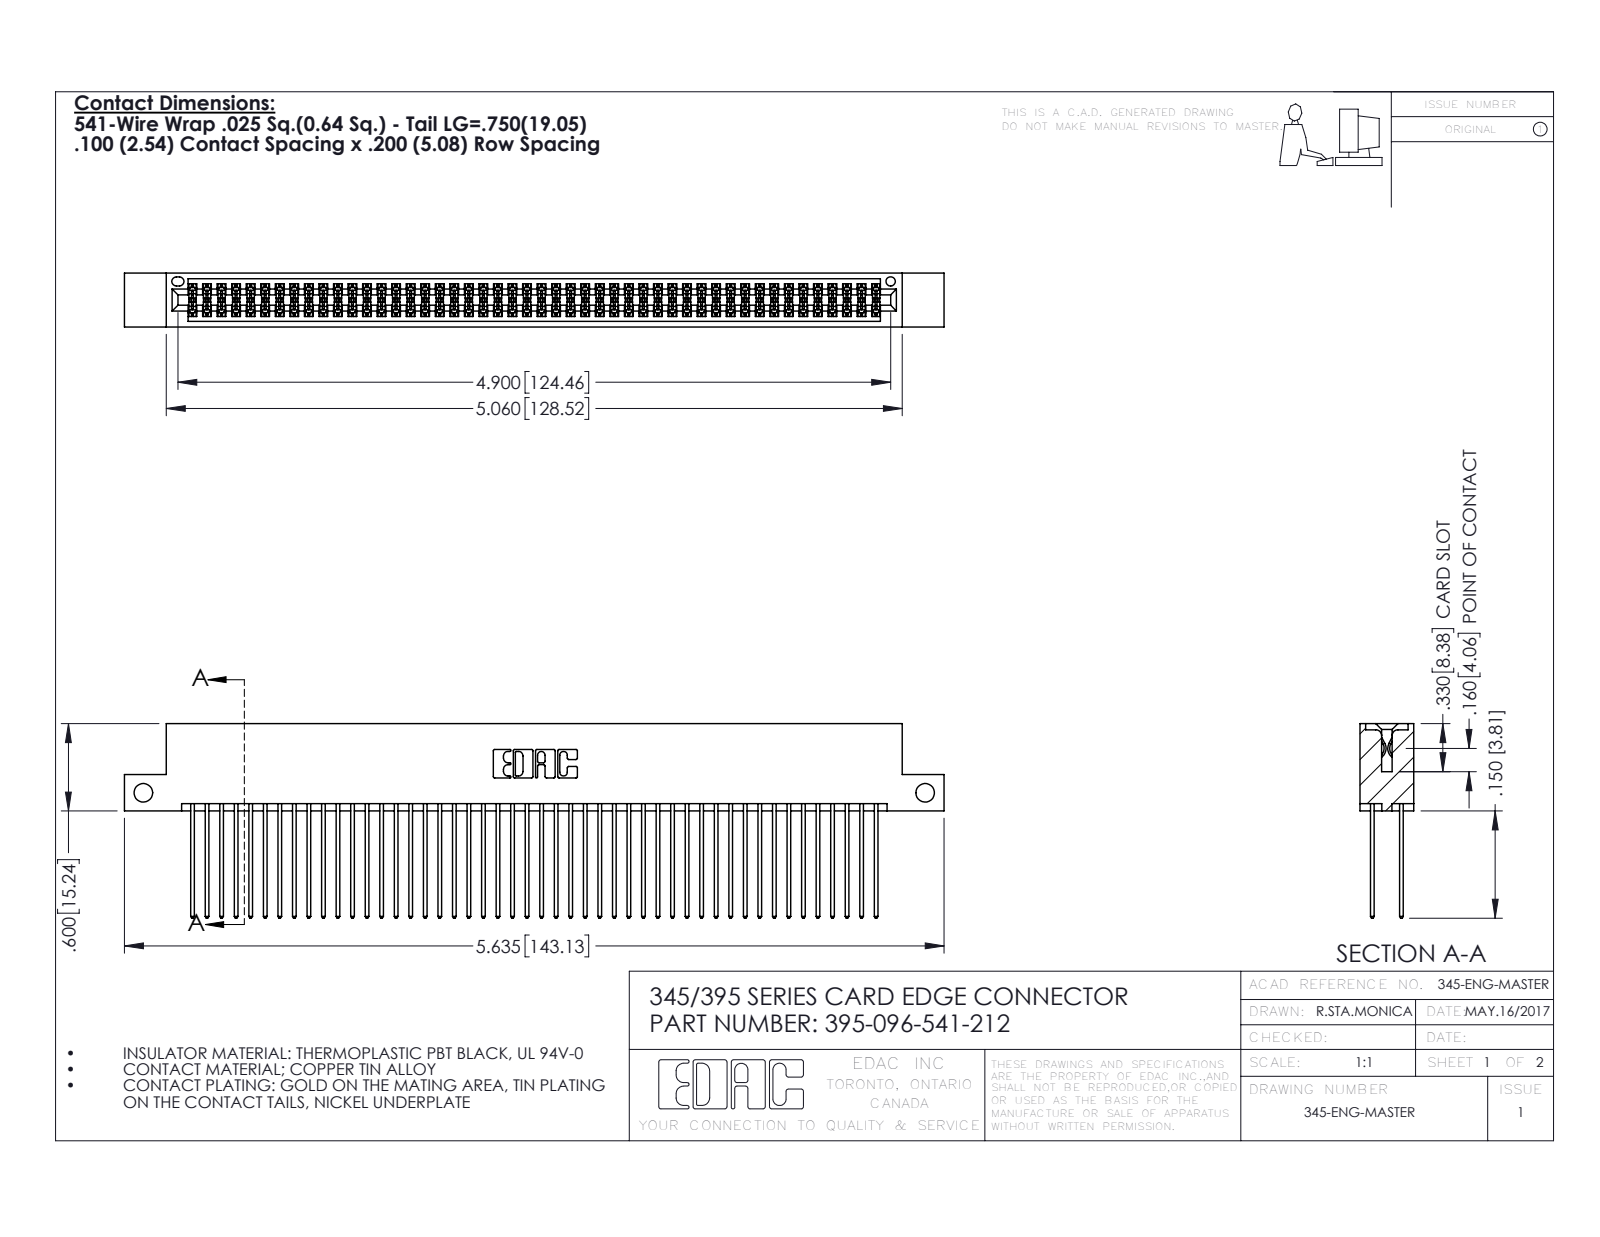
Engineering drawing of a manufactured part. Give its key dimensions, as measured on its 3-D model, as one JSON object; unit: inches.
{"part_name": "345-292-001_345-293-141; 395-096-541-212; 345 Part_Flush Mounting Lugs - Side Mount", "step_written_by": "SolidWorks 2016 (CONFIG_CONTROL_DESIGN)", "units": "inches", "bodies": {"solids": 97, "faces": 4926, "planar": 3248, "cylindrical": 1678, "other": 0}, "overall_size": [5.635, 1.337, 0.37], "volume_in3": 0.88, "surface_area_in2": 37.03, "round_holes": [[0.128, 2], [0.064, 1]], "partial_cylinders_radius": [[0.006, 144], [0.01, 96], [0.01, 22], [0.007, 6], [0.031, 6], [0.026, 3], [0.014, 2], [0.019, 2]], "face_to_face_distances": [0.298, 0.072, 0.2, 0.098, 0.272, 0.025, 0.225, 0.37, 0.175, 0.149], "hole_center_spacings": [5.375]}
